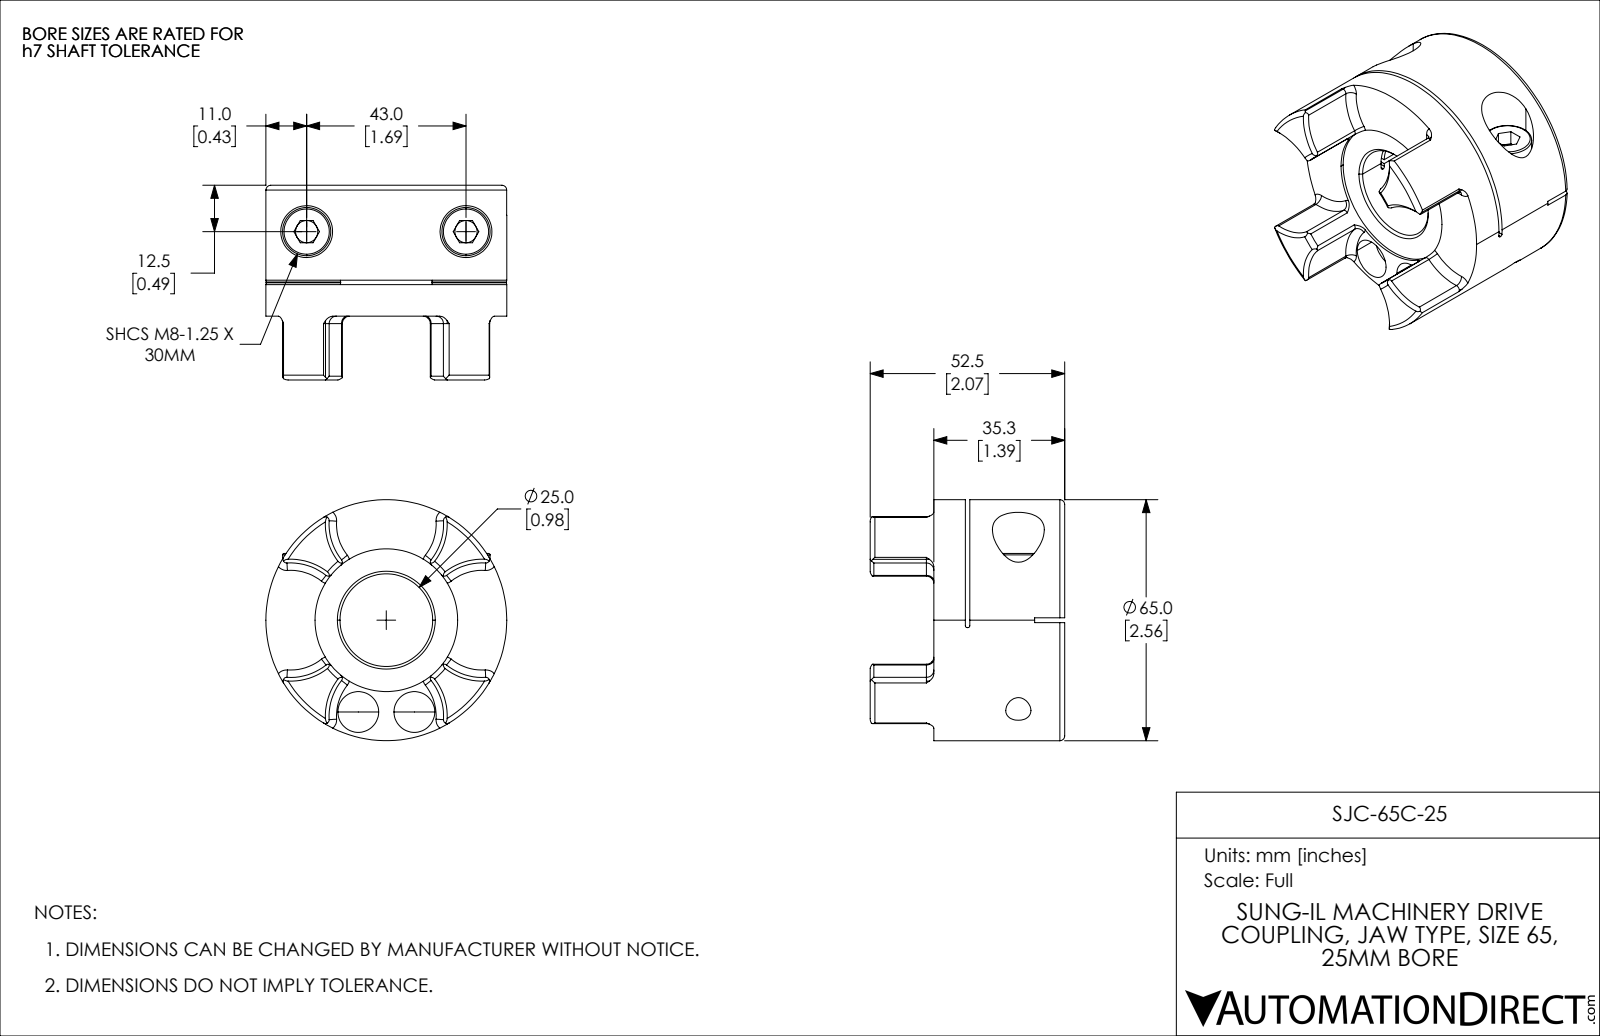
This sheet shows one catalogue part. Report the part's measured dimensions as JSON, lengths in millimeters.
{"part_name": "SJC-65C-25", "step_written_by": "SolidWorks 2021 (CONFIG_CONTROL_DESIGN)", "units": "millimeters", "bodies": {"solids": 3, "faces": 207, "planar": 52, "cylindrical": 73, "other": 82}, "overall_size": [65, 65, 52.5], "volume_mm3": 101774, "surface_area_mm2": 28581, "round_holes": [[6, 2], [6.8, 2], [8.5, 2], [11, 2], [14, 2], [25, 1], [38.5, 1]], "round_bosses_or_shafts": [[13, 2], [8, 2], [65, 1]], "partial_cylinders_radius": [[1, 16], [15.45, 4], [0.5, 2], [50, 1]], "face_to_face_distances": [26.8, 1.2, 25.6, 8.5, 9.7, 35.3, 1.3, 0.8, 7.7, 8.9], "hole_center_spacings": [25.89, 15.14, 43]}
